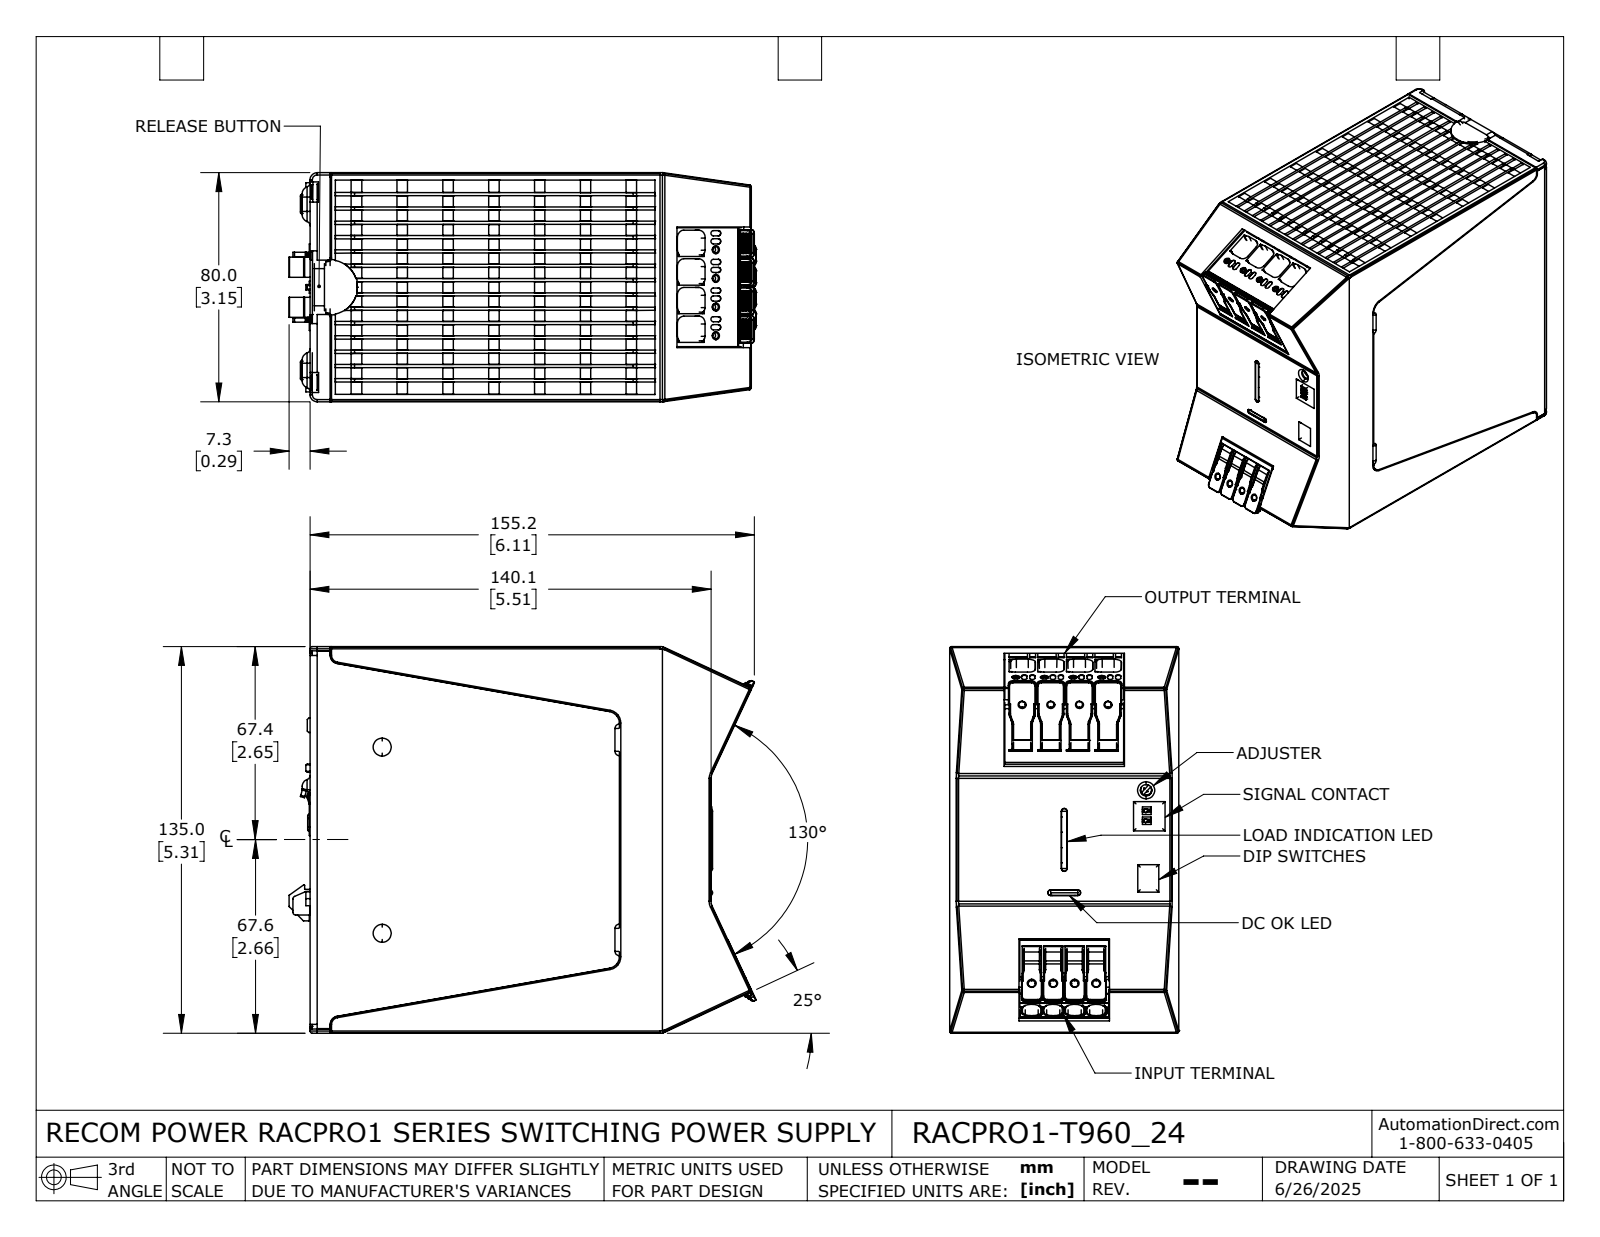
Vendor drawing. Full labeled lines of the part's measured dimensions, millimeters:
Part name (STEP PRODUCT): RACPRO1-T960_24
STEP written by: SolidWorks 2024 (AUTOMOTIVE_DESIGN)
Units: millimetres
Bodies: 1 solid, 5159 faces (2593 planar, 1523 cylindrical, 1043 other)
Overall size (bounding box): 163.2 × 135 × 80
Volume: 1 518 000 mm³ · Surface area: 125 600 mm²
Round holes (diameter × count): ⌀2.2 ×8, ⌀2.5 ×4, ⌀2 ×2, ⌀4 ×1, ⌀4.9 ×1
Round bosses / shafts (diameter × count): ⌀5 ×2, ⌀3.8 ×1
Partial cylindrical surfaces — rounded edges, fillets, slot ends (radius × count): R0.2 ×213, R0.3 ×113, R1 ×54, R0.3 ×50, R0.5 ×49, R3 ×48, R0.2 ×32, R2.5 ×31
Main face-to-face distances: 80, 1.5, 78.5, 0.5, 133.3, 134, 134.5, 140.1, 1, 0.7
Hole centre spacings: 10, 20, 7.5, 15, 30, 22.5, 38.2, 68
